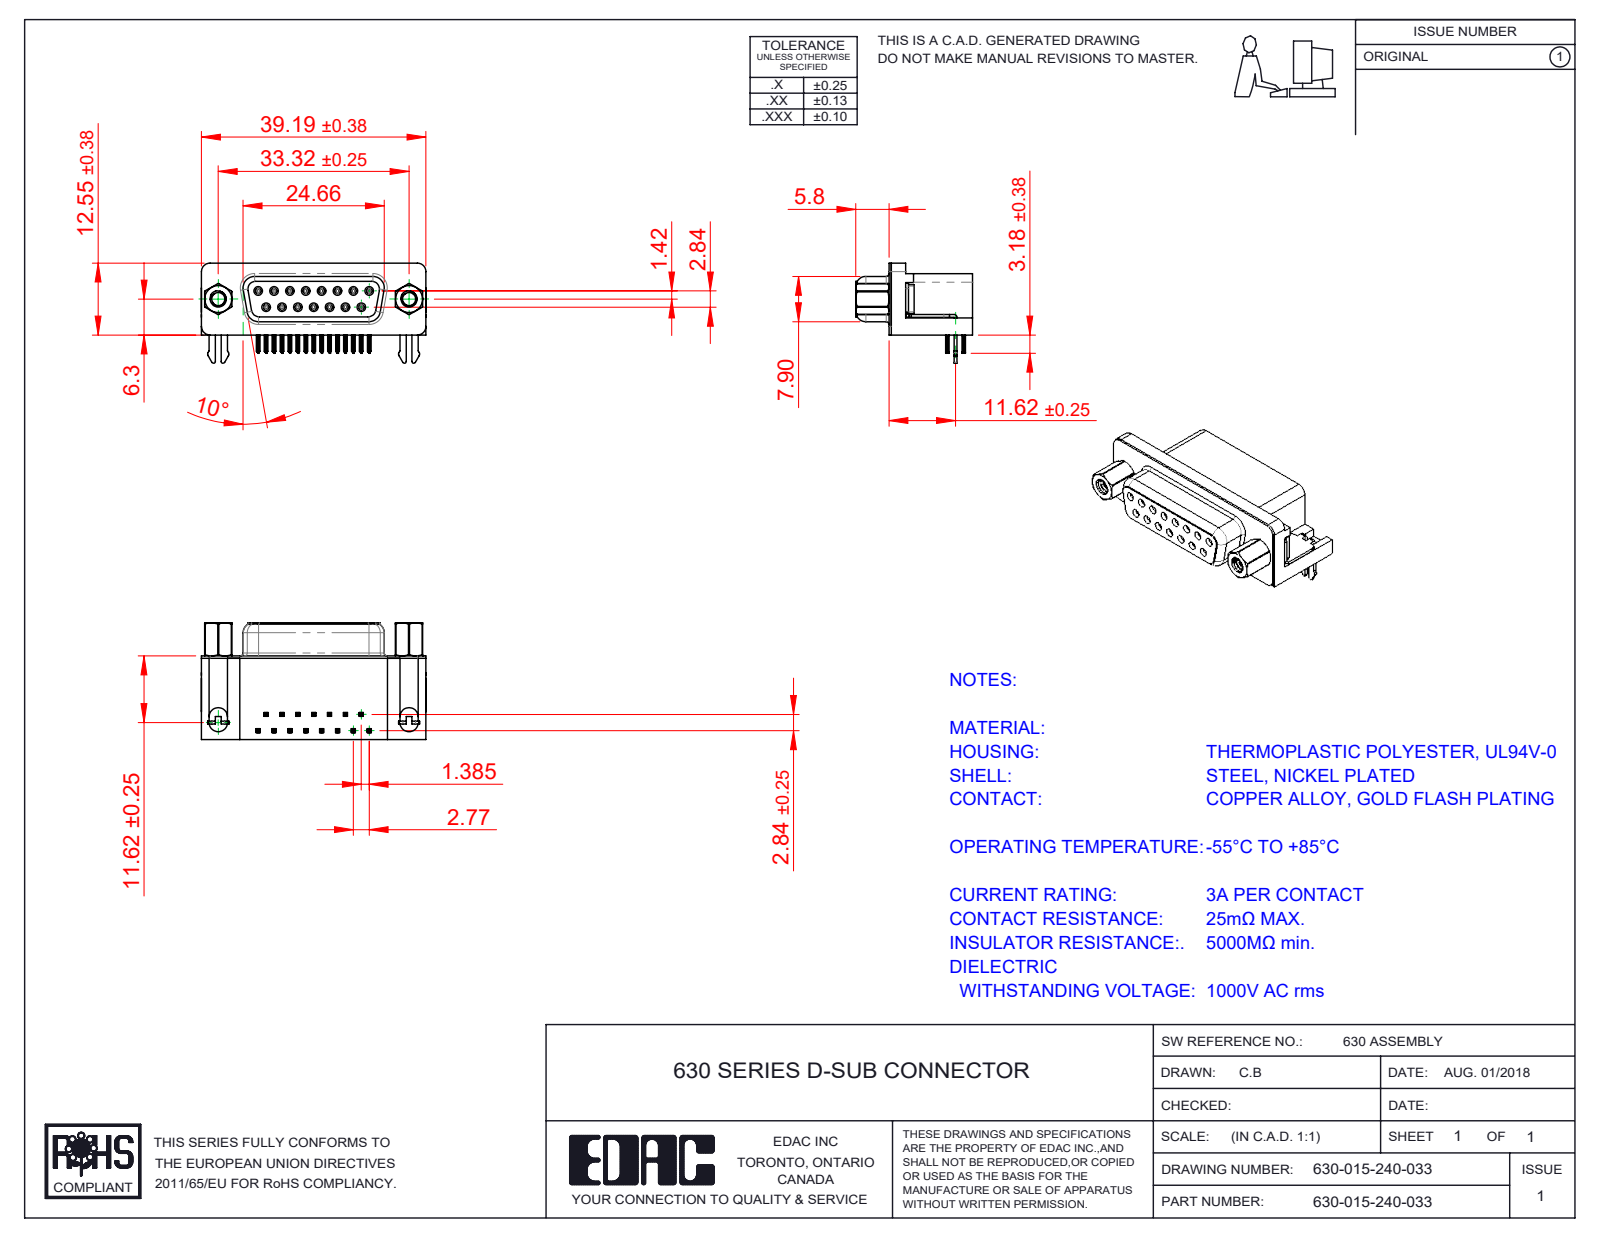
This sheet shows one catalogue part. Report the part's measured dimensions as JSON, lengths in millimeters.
{"part_name": "630 Contact Bottom; 630-015-240-033; 630 Housing_15 Socket; 630 Contact Top (+4 more)", "step_written_by": "SolidWorks 2020 (CONFIG_CONTROL_DESIGN)", "units": "millimeters", "bodies": {"solids": 23, "faces": 2591, "planar": 1126, "cylindrical": 685, "other": 780}, "overall_size": [39.22, 20.4, 17.48], "volume_mm3": 6073, "surface_area_mm2": 7688, "round_holes": [[0.8, 15], [0.9, 15], [2.26, 2], [2.29, 2], [4, 2], [4.8, 2], [5, 2]], "round_bosses_or_shafts": [[1.2, 15], [4.9, 2], [4.75, 2], [3.9, 2], [2.79, 2]], "partial_cylinders_radius": [[0.1, 120], [0.15, 60], [0.35, 30], [1, 18], [0.34, 15], [0.5, 10], [0.25, 8], [1.35, 8]], "face_to_face_distances": [0.4, 6.2, 2.73, 14.2, 10.35, 14.6, 2.9, 3.18, 5.8, 6.65], "hole_center_spacings": [3.16, 2.77, 5.54, 5.03, 5.04, 7.48, 7.49, 8.31]}
